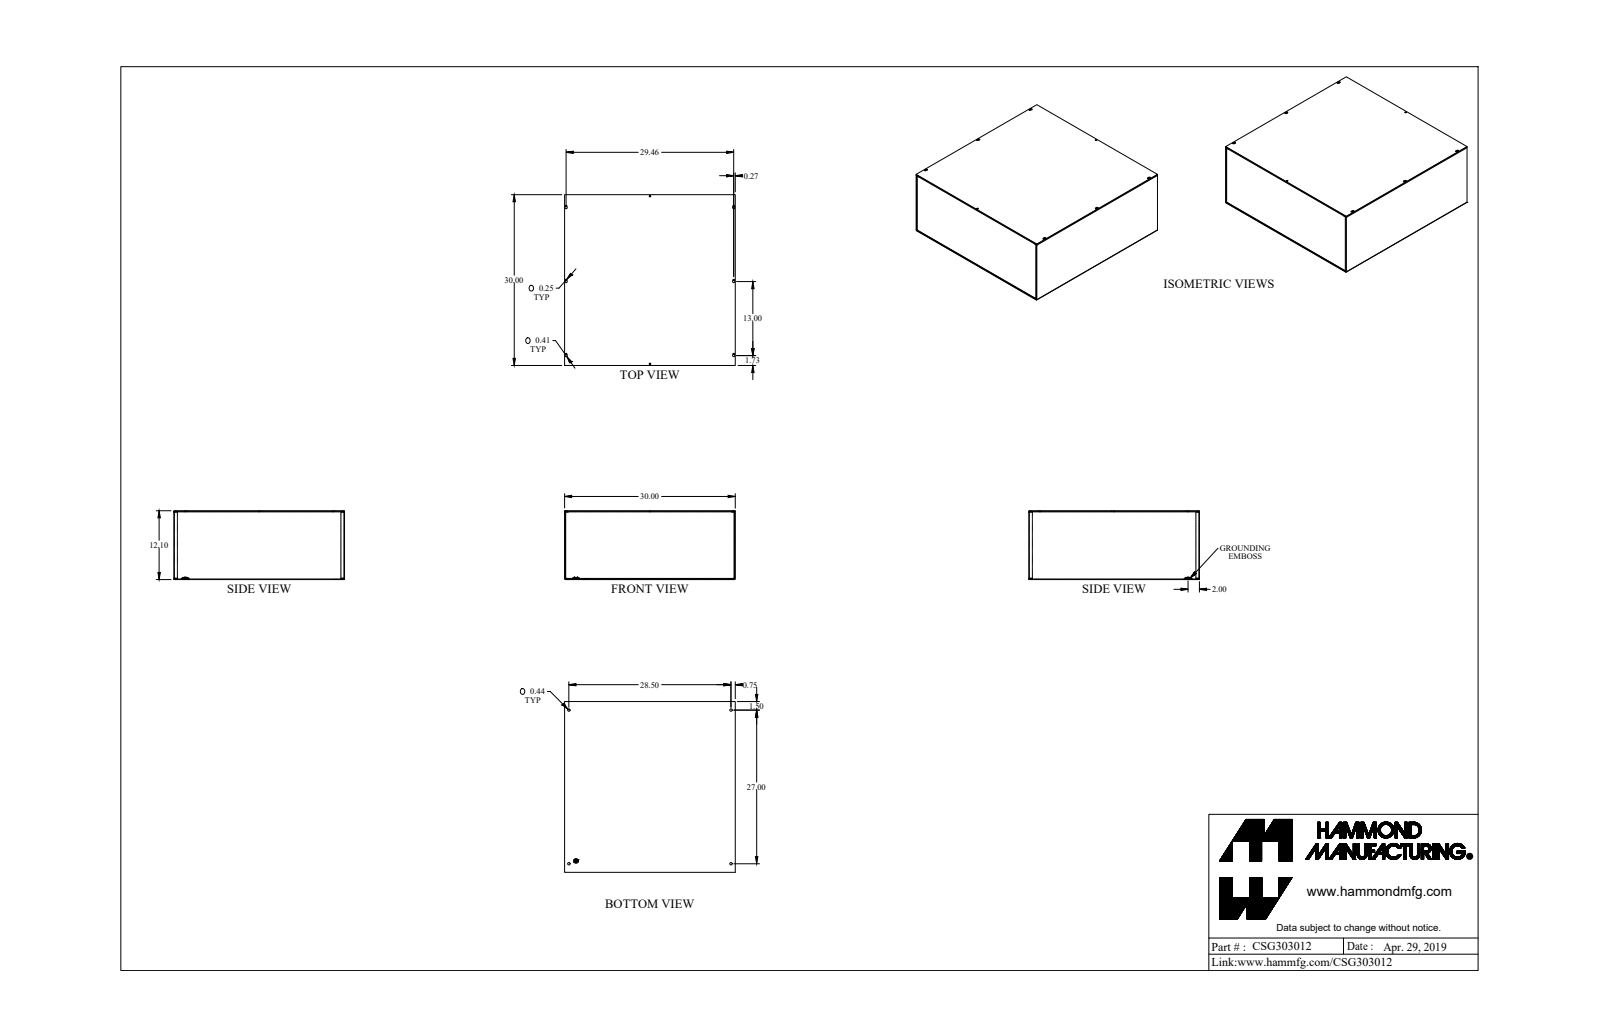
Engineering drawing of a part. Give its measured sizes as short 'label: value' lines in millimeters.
name: CSG303012_Default
written by: SolidWorks 2019 (CONFIG_CONTROL_DESIGN)
unit: mm
bodies: 4 solids, 221 faces (121 planar, 92 cylindrical, 8 other)
size: 762 × 762 × 307.2
volume: 5 157 000 mm³; area: 4 305 000 mm²
holes: 9× ⌀4.3, 4× ⌀11.1, 2× ⌀6.4, 1× ⌀12.7
bosses: 1× ⌀12.5, 1× ⌀9.1
rounds: 12× R1.2, 12× R3.6, 8× R2.4, 6× R3.2, 6× R5.2
face distances: 2.4, 304.8, 759.6, 302.4, 307.2, 762, 757.2, 2.7, 756.9, 4.8
hole spacings: 17.6, 330.2, 343.1, 363.3, 376.7, 529.1, 673.2, 736.2
